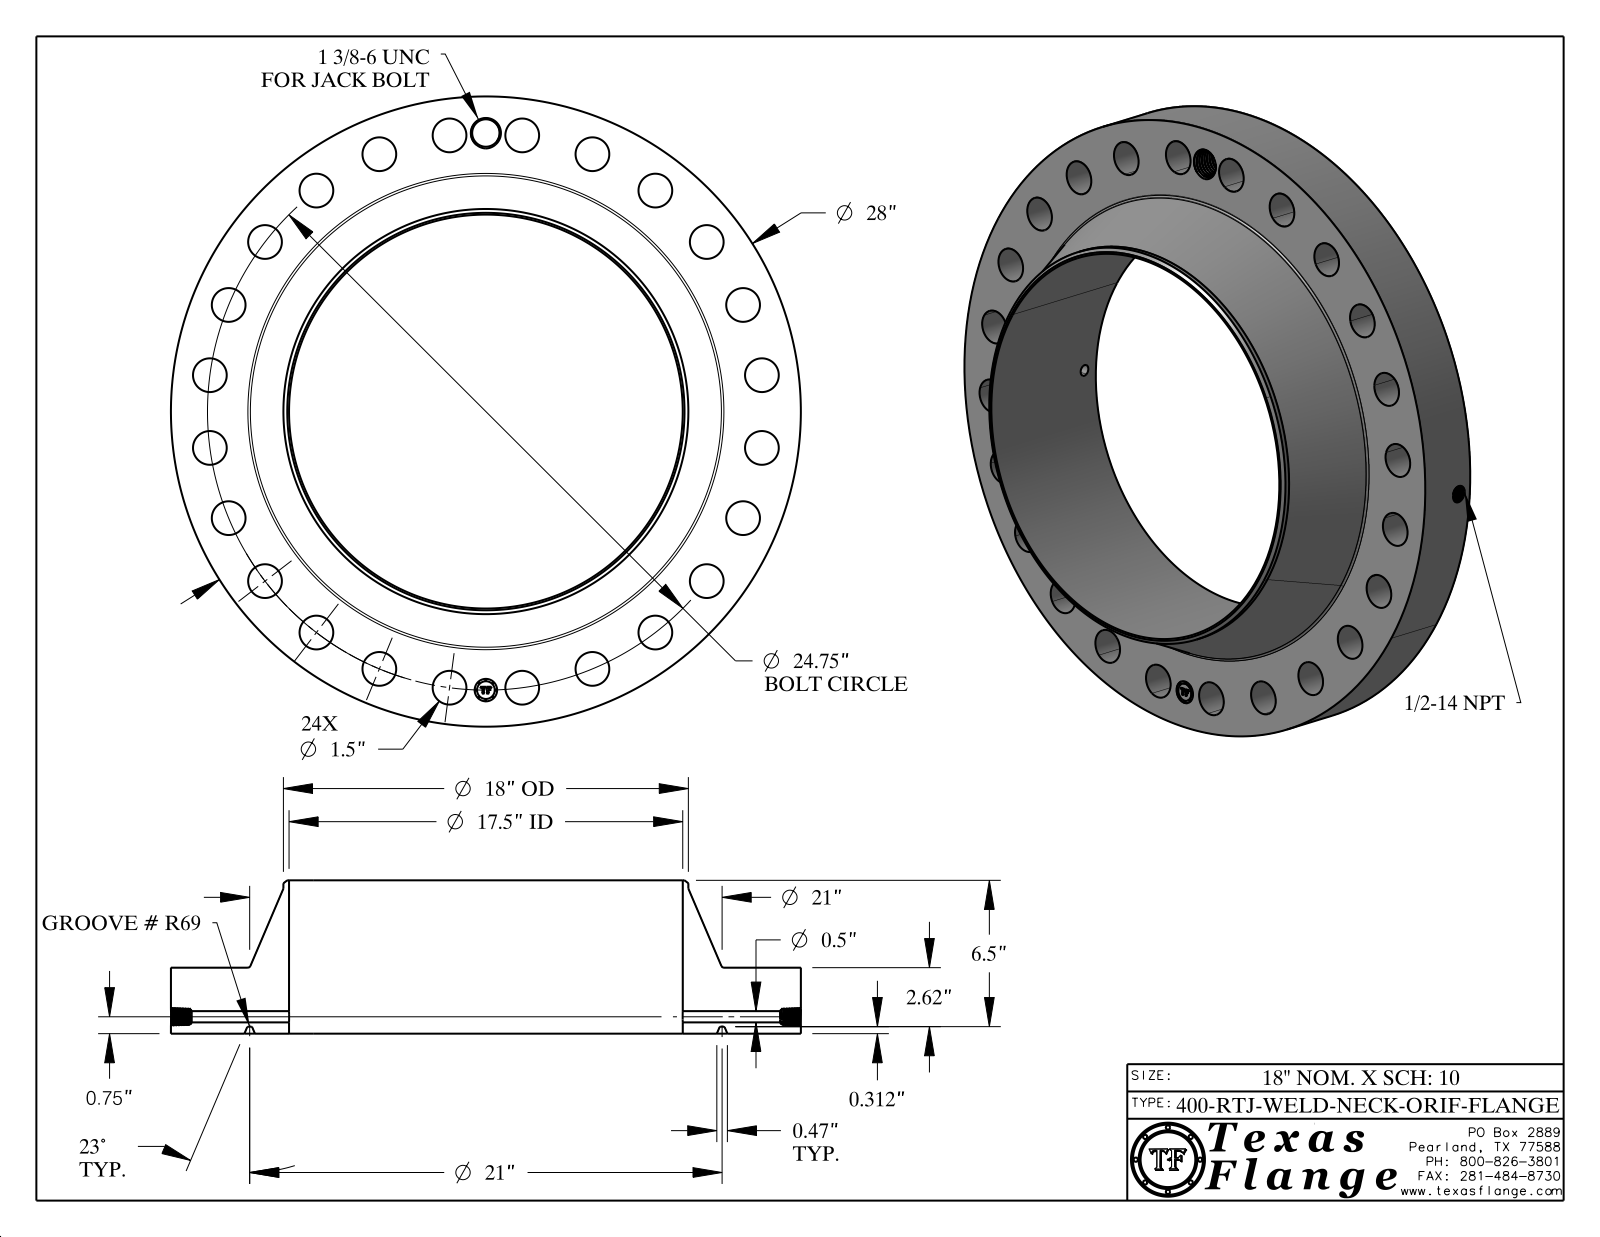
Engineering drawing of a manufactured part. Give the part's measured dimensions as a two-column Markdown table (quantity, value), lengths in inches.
| quantity | value |
| --- | --- |
| part name | 400-RTJ-WELD-NECK |
| STEP written by | CATIA V5 STEP AP214 (AUTOMOTIVE_DESIGN) |
| units | inches |
| bodies | 1 solid, 824 faces (370 planar, 129 cylindrical, 325 other) |
| overall size | 28 × 28 × 6.812 |
| volume | 1 173 in³ |
| surface area | 1 847 in² |
| round holes (diameter × count) | 1.5 × 24, 0.5 × 1, 0.672 × 1, 1 × 1, 1.219 × 1, 17.5 × 1 |
| round bosses / shafts (diameter × count) | 0.061 × 8, 28 × 1, 18 × 1, 0.788 × 1 |
| main face-to-face distances | 2.932, 0.312, 2.62, 6.812, 6.5, 3.88, 0.015, 2.917, 2.605, 3.895 |
| hole center spacings | 12.375, 15.067, 21.434, 22.866, 23.907, 6.406, 17.501, 3.23 |
